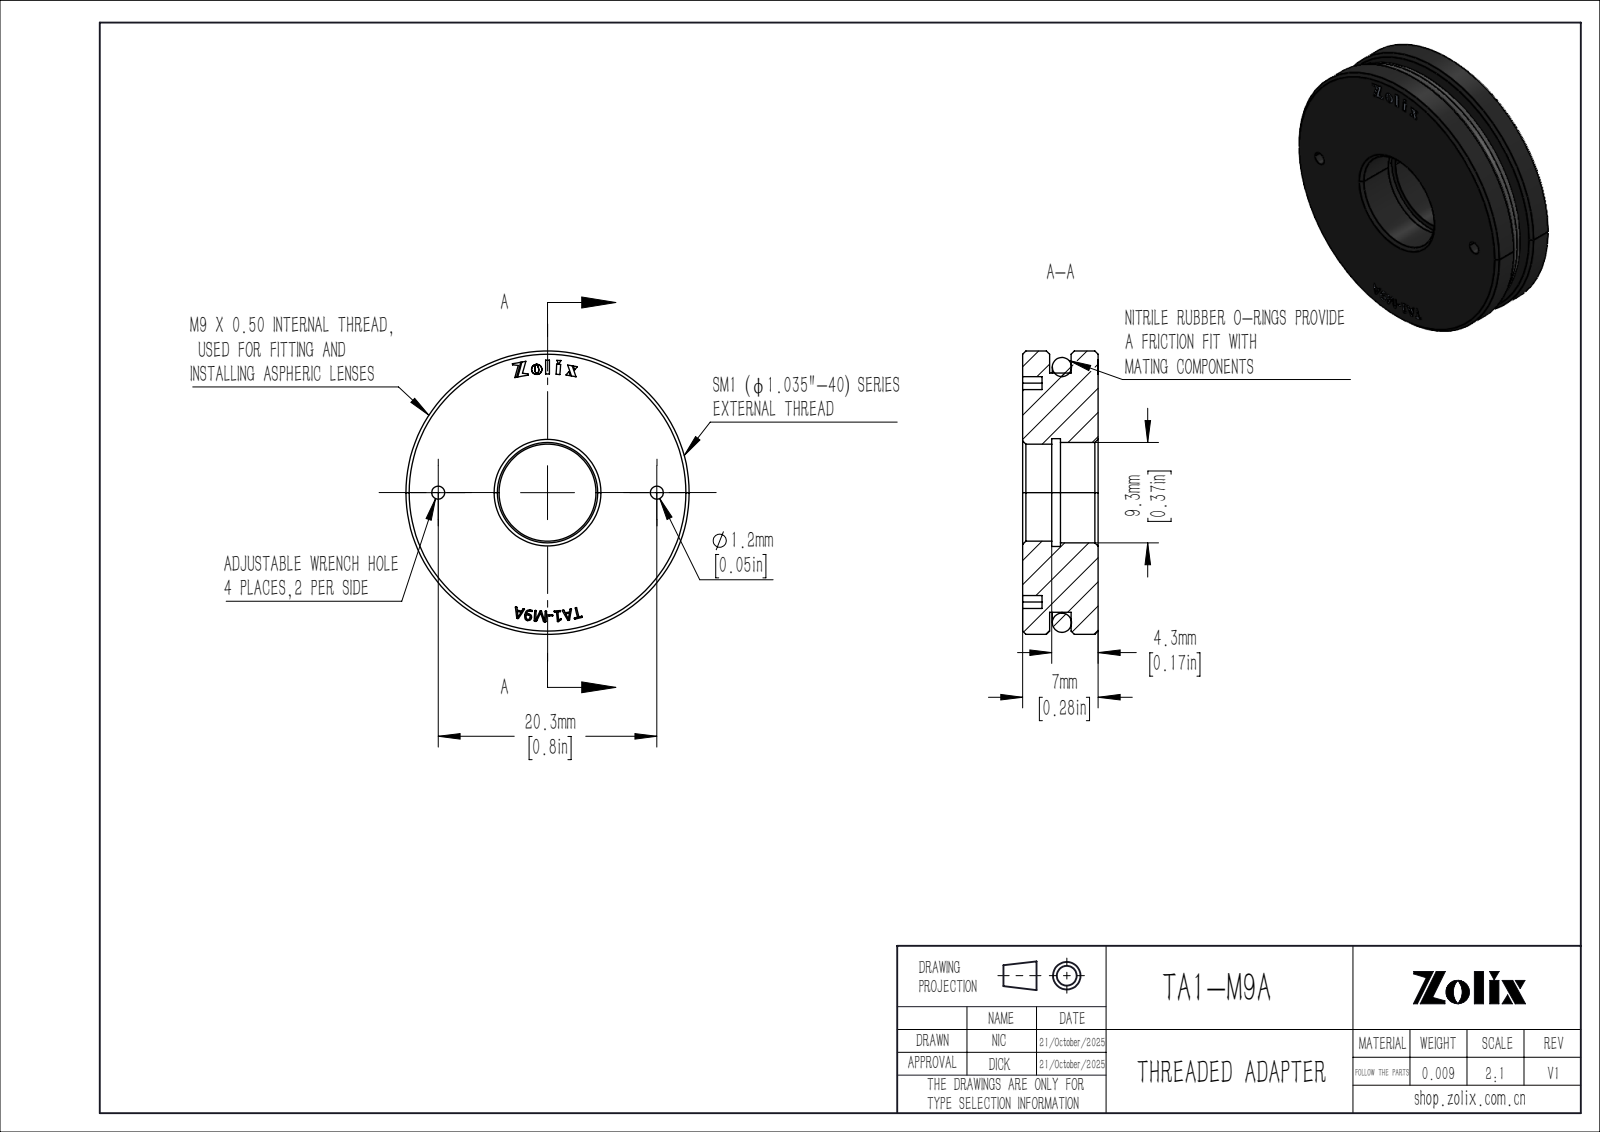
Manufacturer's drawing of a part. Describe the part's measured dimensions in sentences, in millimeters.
The part is named "TA1-M9A". Its 3-D file was written by "SolidWorks 2020 (CONFIG_CONTROL_DESIGN)". It is 2 solids with 312 faces: 214 planar, 20 cylindrical and 78 other. Overall it measures 26.29 by 26.29 by 7 millimeters. Its volume is 3 176 cubic millimeters and its surface area 2 424 square millimeters. Round holes: 4 of diameter 1.2, 1 of diameter 9, 1 of diameter 9.3, 1 of diameter 10. Round bosses or shafts: 1 of diameter 26.29, 1 of diameter 22.2. The main face-to-face distances are 7, 2.5, 4.5, 2, 3.5, 1, 1.8, 2.7, 4.3, 0.8. The hole center spacings are 10.15, 14.35, 20.3.
